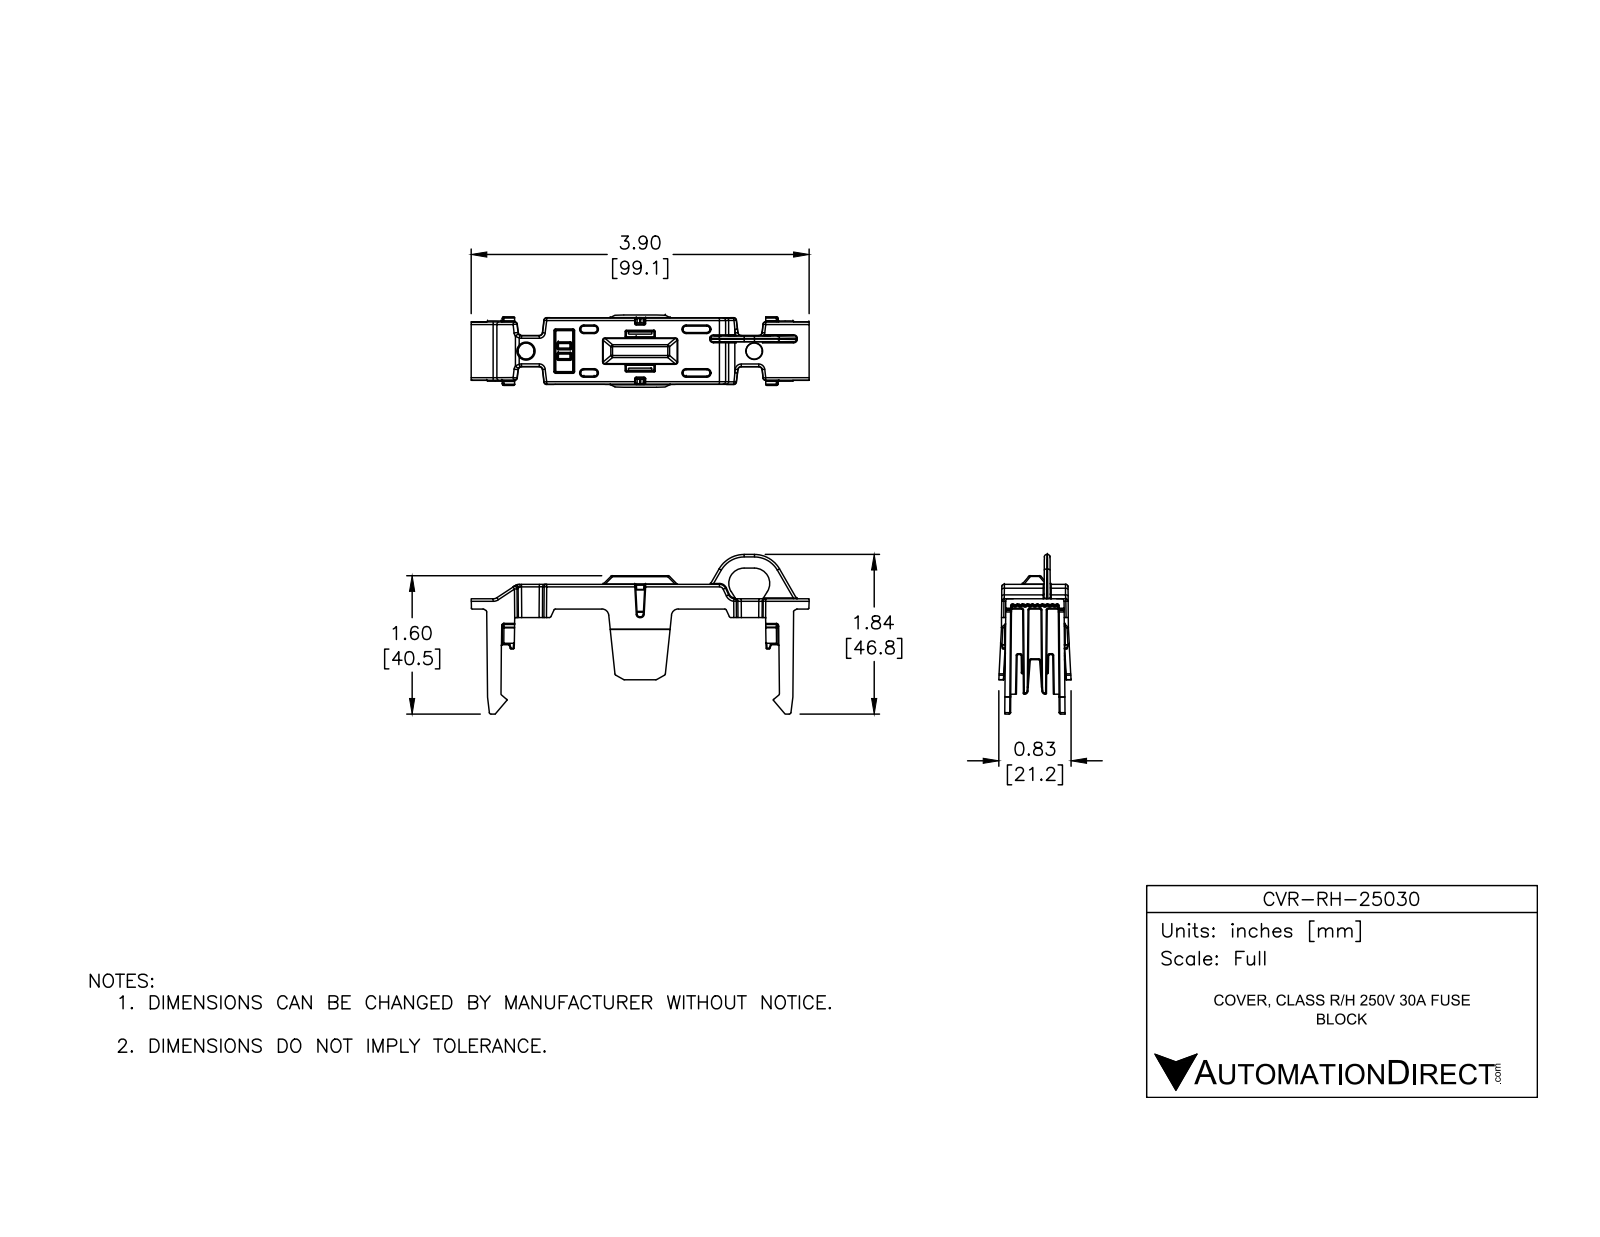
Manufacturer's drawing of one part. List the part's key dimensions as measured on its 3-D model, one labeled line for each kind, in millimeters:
Part name (STEP PRODUCT): CVR-RH-25030
STEP written by: SolidWorks 2016 (AUTOMOTIVE_DESIGN)
Units: millimetres
Bodies: 1 solid, 2459 faces (431 planar, 1074 cylindrical, 954 other)
Overall size (bounding box): 99.1 × 46.8 × 21.2
Volume: 9 140 mm³ · Surface area: 12 430 mm²
Partial cylindrical surfaces — rounded edges, fillets, slot ends (radius × count): R0.3 ×320, R0.2 ×277, R0.8 ×48, R1 ×39, R0.2 ×38, R0.5 ×18, R0.5 ×9, R0.4 ×8
Main face-to-face distances: 1.5, 1.5, 1.2, 2.5, 0.3, 2.7, 4, 83.1, 4.2, 2.9
